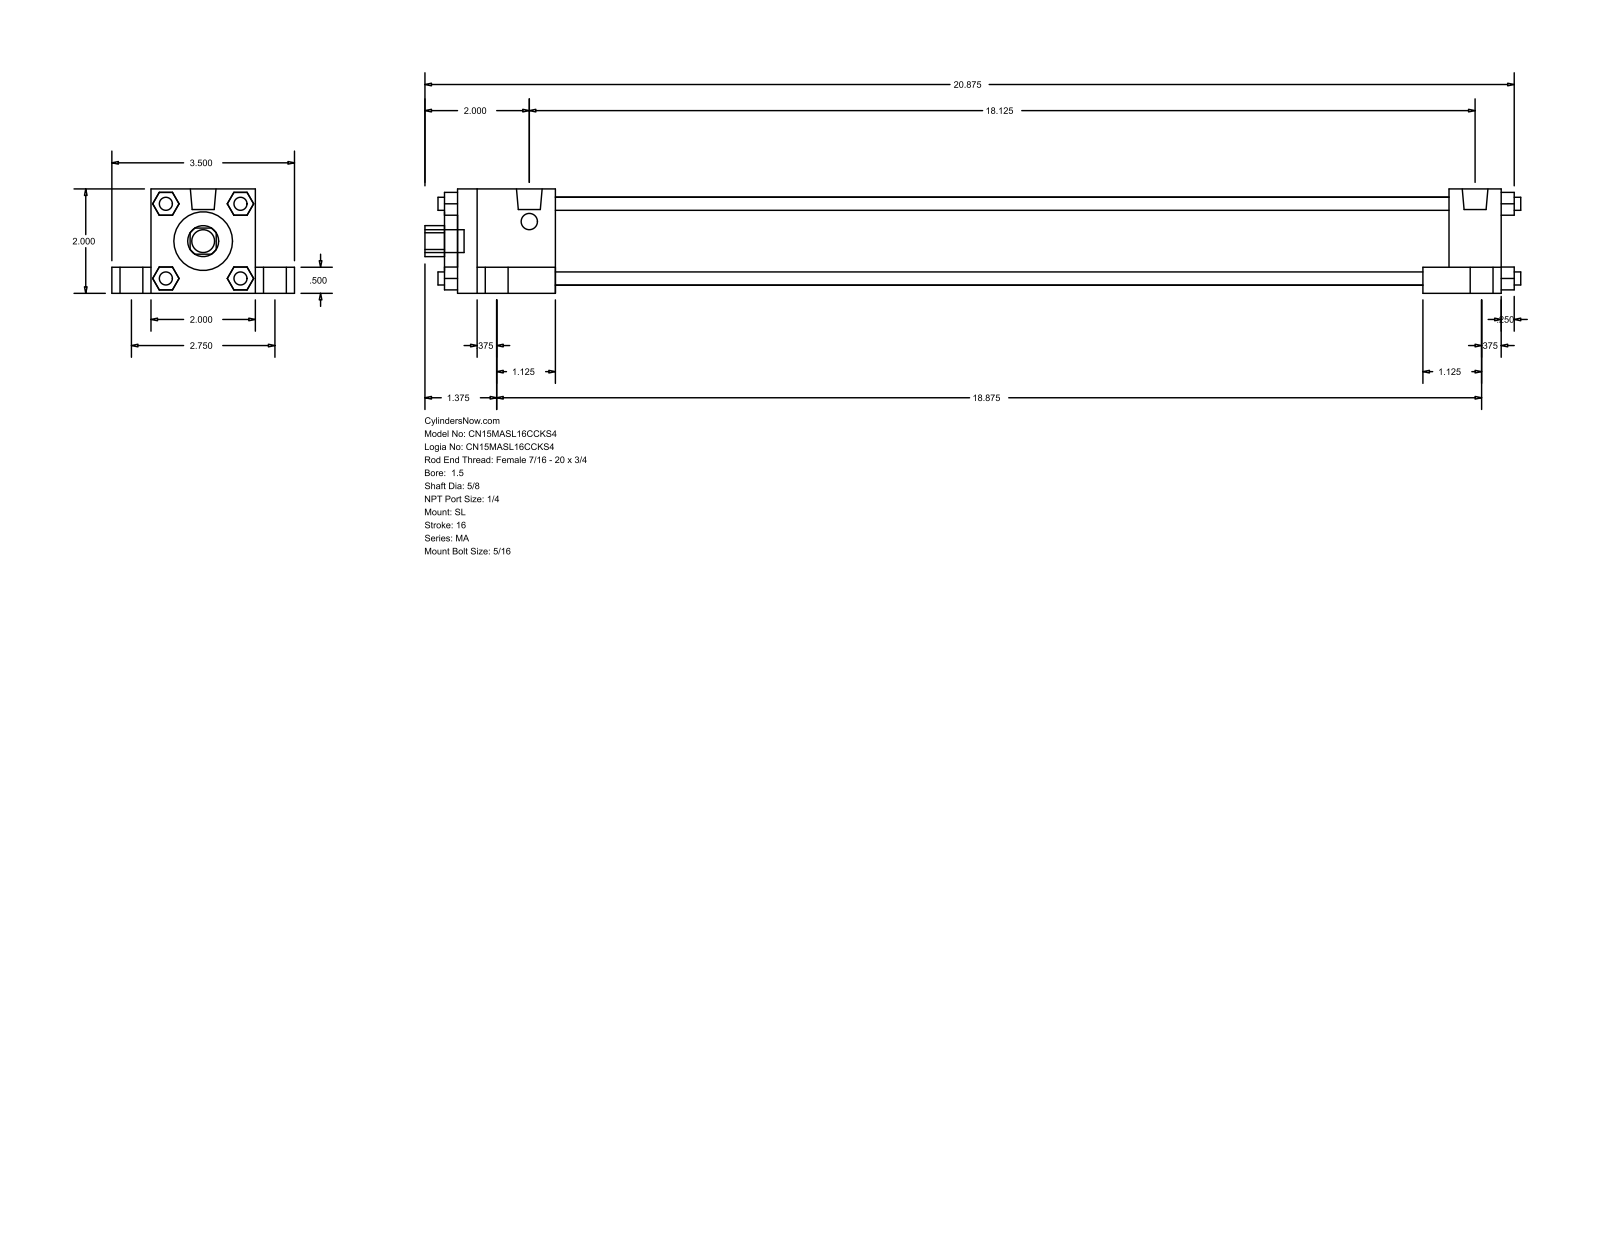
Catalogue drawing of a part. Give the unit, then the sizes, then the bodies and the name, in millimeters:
Units: millimetres
Overall size (bounding box): 533.4 × 88.9 × 50.8
Round holes (diameter × count): ⌀15.88 ×1, ⌀28.57 ×1, ⌀42.93 ×1
Round bosses / shafts (diameter × count): ⌀11.11 ×5, ⌀17.46 ×4, ⌀7.94 ×4, ⌀6.35 ×4, ⌀12.49 ×2
Partial cylindrical surfaces — rounded edges, fillets, slot ends (radius × count): R7.54 ×1
Main face-to-face distances: 50.8, 19.05, 38.1, 12.7, 508, 69.85, 9.52, 6.35, 514.35, 25.4
Bodies: 0 solids, 148 faces (112 planar, 36 cylindrical, 0 other)
Part name (STEP PRODUCT): MA_SL__0150_0.625
STEP written by: GSSL Pune (CONFIG_CONTROL_DESIGN)
